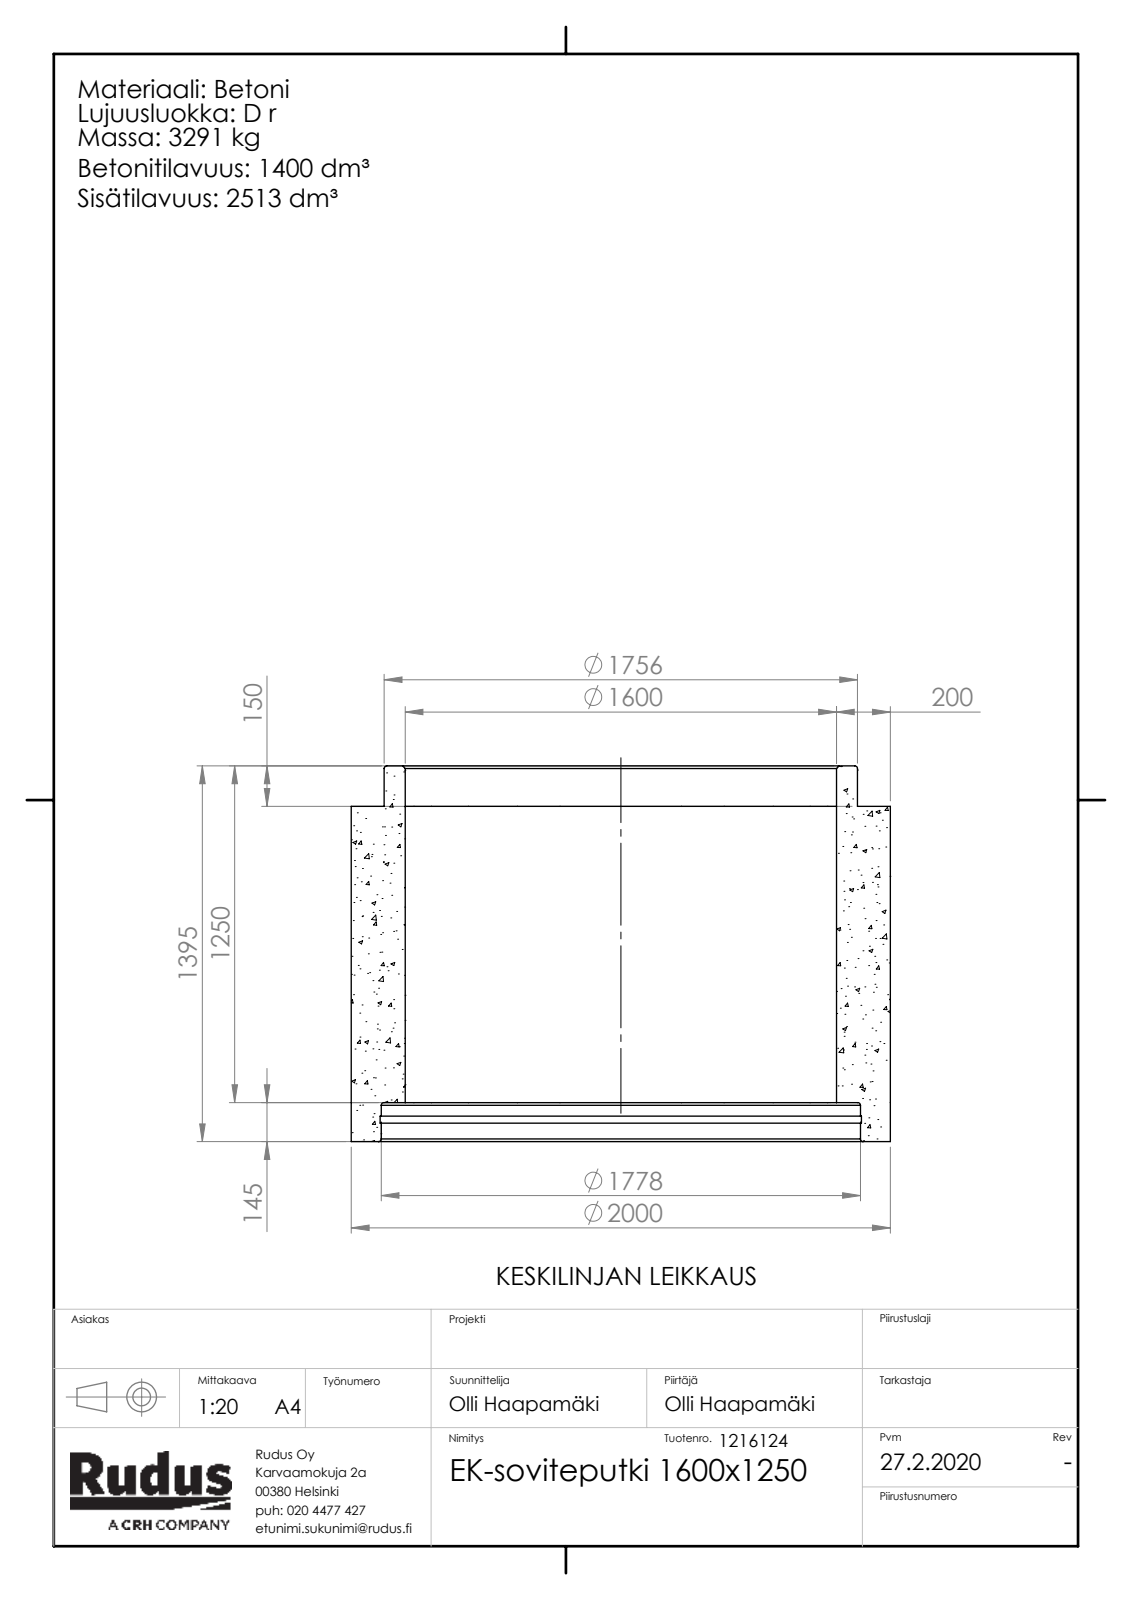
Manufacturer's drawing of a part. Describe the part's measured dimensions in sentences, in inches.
The part is named "Rudus 1216124 EK-soviteputki 1600x1250; EK-osa-putkirunko". Its 3-D file was written by "SolidWorks 2019 (CONFIG_CONTROL_DESIGN)". It is 1 solid with 107 faces: 9 planar, 12 cylindrical and 86 other. Overall it measures 78.74 by 78.74 by 54.921 inches. Its volume is 85 490 cubic inches and its surface area 27 820 square inches. Round holes: 1 of diameter 62.992, 1 of diameter 70, 1 of diameter 70.315. Round bosses or shafts: 1 of diameter 78.74, 1 of diameter 69.142. The main face-to-face distances are 49.016, 5.709, 43.307, 54.921, 49.213, 5.906, 2.717, 3.74, 1.024, 2.992.
